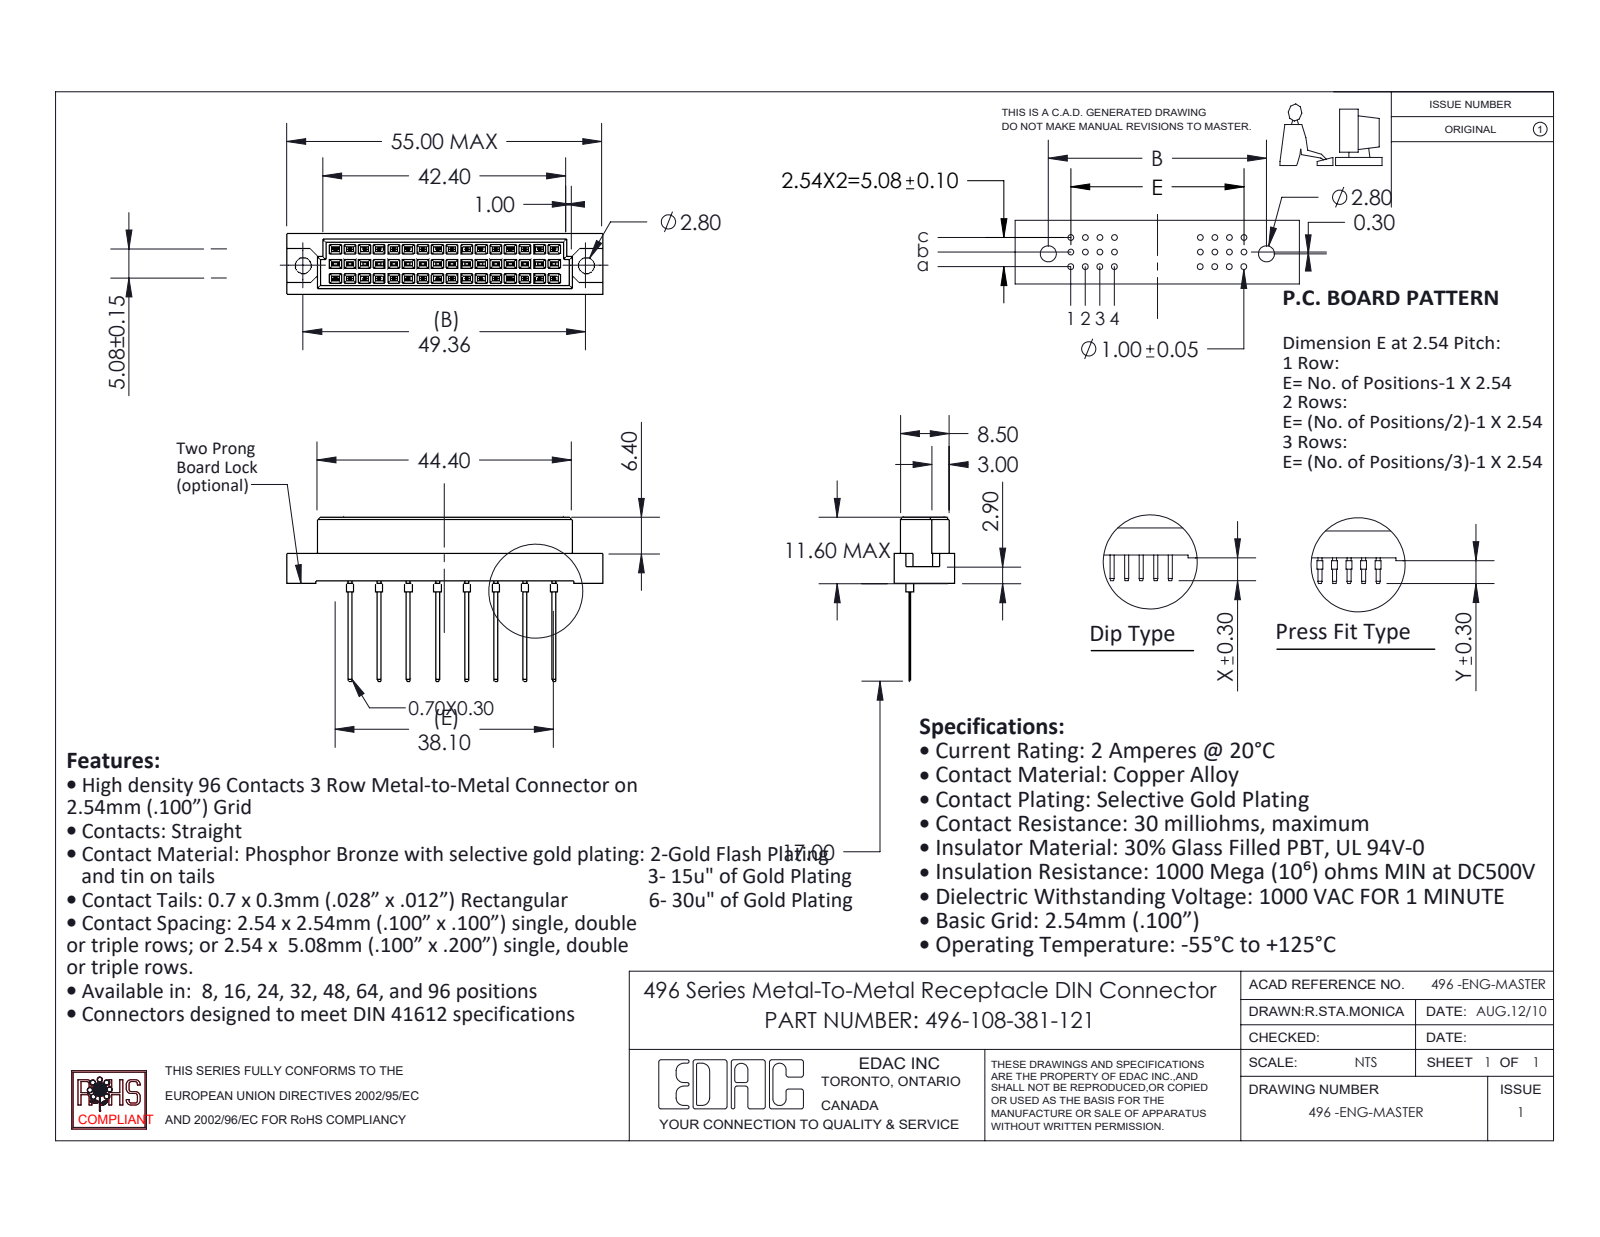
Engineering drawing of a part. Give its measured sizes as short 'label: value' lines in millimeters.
name: 496-108-381-121; 496-290_81; 496 Part_48
written by: SolidWorks 2020 (CONFIG_CONTROL_DESIGN)
unit: mm
bodies: 9 solids, 810 faces (790 planar, 20 cylindrical, 0 other)
size: 55 × 28.6 × 10.6
volume: 4 633 mm³; area: 4 588 mm²
holes: 2× ⌀2.8
bosses: 8× ⌀1
face distances: 2.54, 5.08, 1.05, 9.55, 0.81, 10.6, 3.35, 1.73, 8.5, 0.56
hole spacings: 49.36
